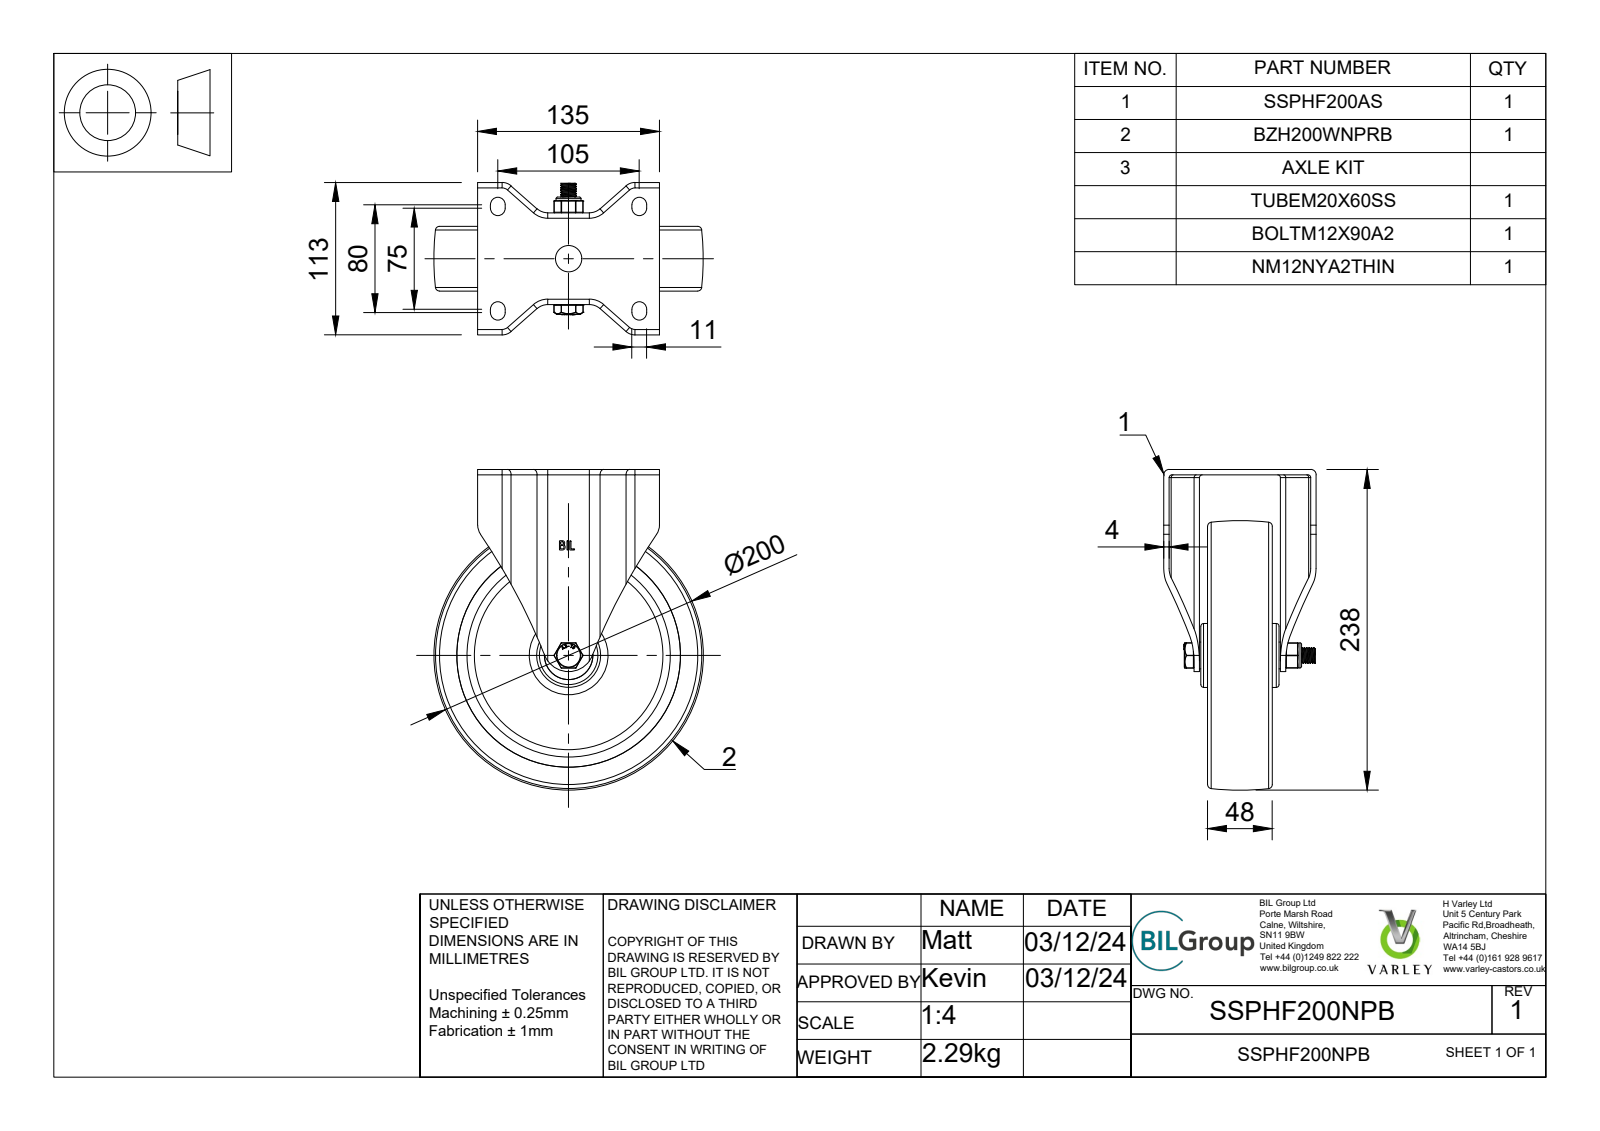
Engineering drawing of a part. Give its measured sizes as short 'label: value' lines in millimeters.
name: SSPHF200NPB v3; SSPHF200AS v1; STAINLESS STEEL BRACKET; BZH200WNPRB v1 (+7 more)
written by: Autodesk Translation Framework v13.20.0.188 (AP242_MANAGED_MODEL_BASED_3D_ENGINEERING_MIM_LF)
unit: mm
bodies: 17 solids, 483 faces (190 planar, 173 cylindrical, 120 other)
size: 238 × 200 × 113
volume: 1 035 000 mm³; area: 290 055 mm²
holes: 1× ⌀12, 1× ⌀12.5, 1× ⌀14, 1× ⌀19.5, 1× ⌀20, 1× ⌀20.5, 1× ⌀21, 1× ⌀35, 1× ⌀36, 1× ⌀151, 1× ⌀166
bosses: 8× ⌀7.5, 1× ⌀47.5, 1× ⌀34, 1× ⌀19.9, 1× ⌀18.5, 1× ⌀17.75, 1× ⌀11.83, 1× ⌀9.84
rounds: 18× R0.5, 12× R0.25, 8× R2, 8× R4, 8× R5.5, 6× R12, 4× R6, 4× R10
face distances: 4, 20, 28, 8, 48, 58, 20.52, 10, 30, 38
